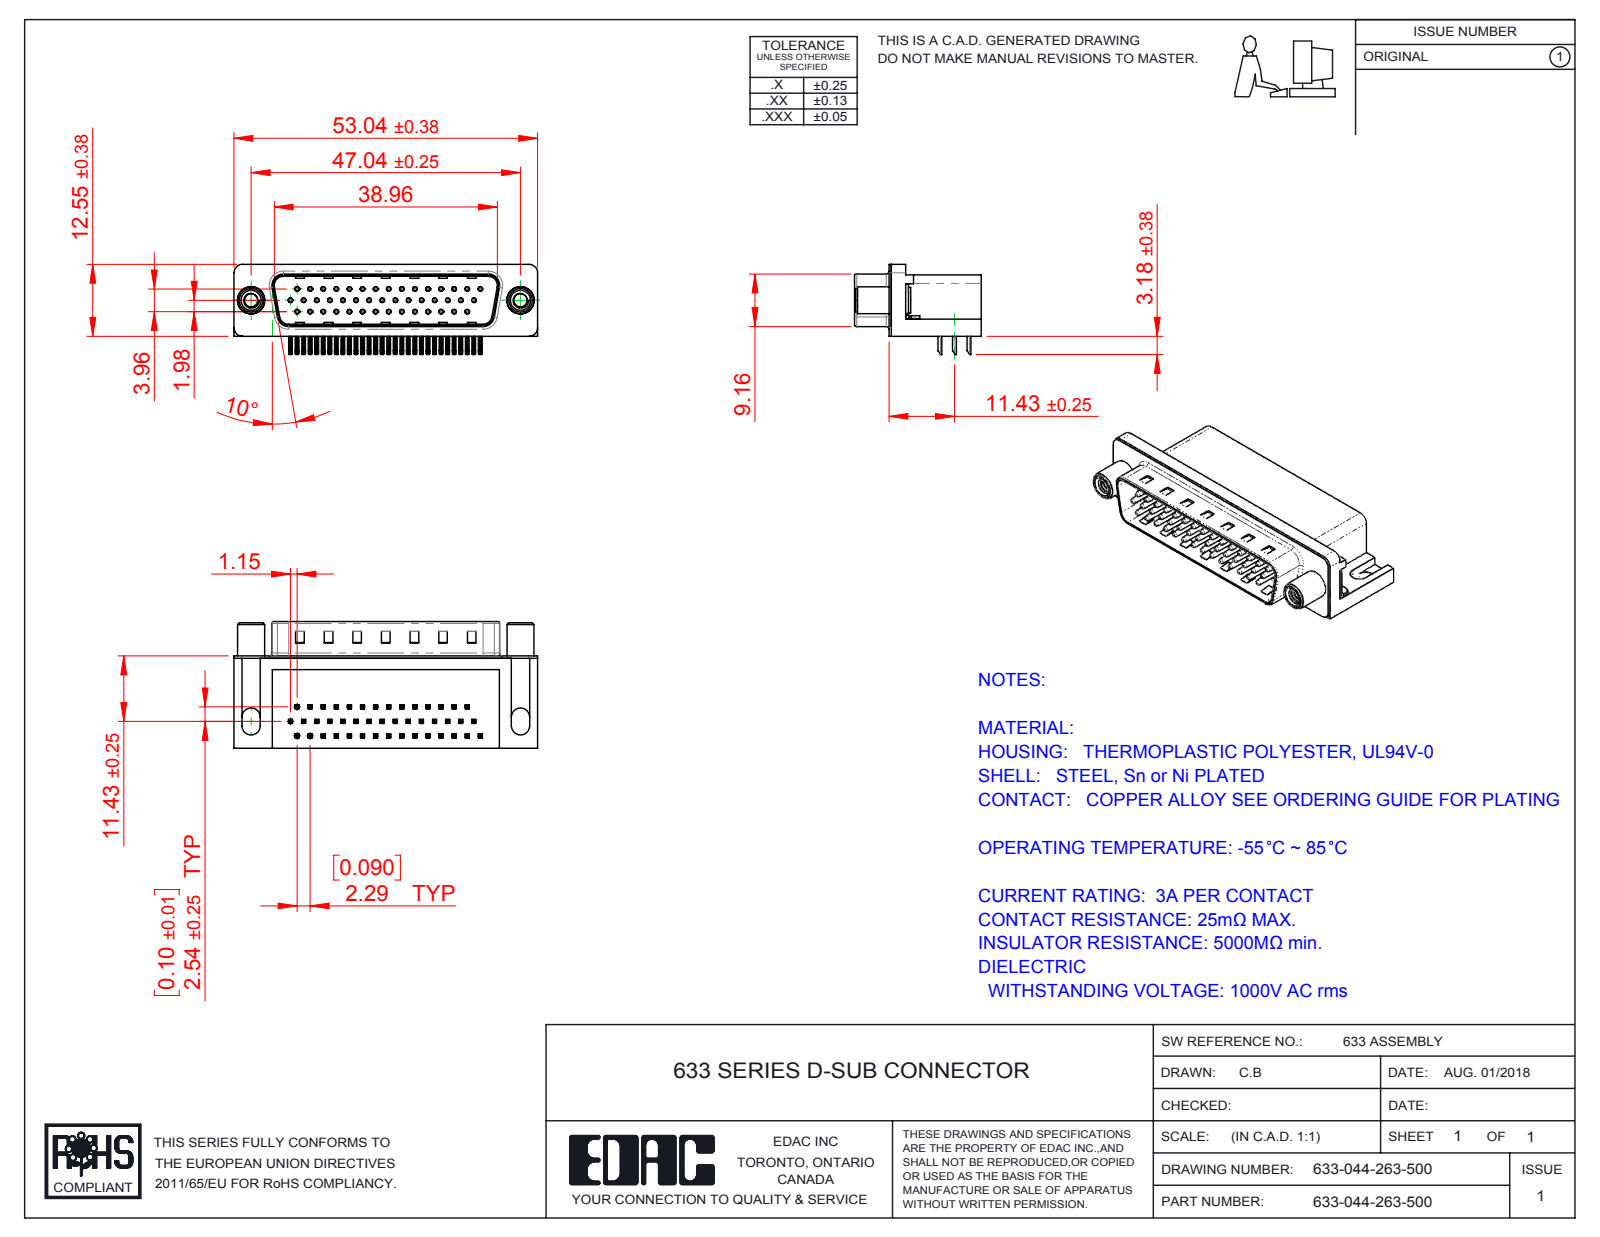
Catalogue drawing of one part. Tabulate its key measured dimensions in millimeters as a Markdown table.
| quantity | value |
| --- | --- |
| part name | 633 Non Board Mount; 633 Round Threaded Standoff; 633 Contact Middle; 633 Shell_44 Contact (+4 more) |
| STEP written by | SolidWorks 2016 (CONFIG_CONTROL_DESIGN) |
| units | millimeters |
| bodies | 50 solids, 3680 faces (2309 planar, 1064 cylindrical, 307 other) |
| overall size | 53.04 × 22.1 × 15.73 |
| volume | 8 158 mm³ |
| surface area | 10 194 mm² |
| round holes (diameter × count) | 0.35 × 44, 0.8 × 44, 2.3 × 2, 3.1 × 2, 4 × 2, 4.8 × 2, 5 × 2 |
| round bosses / shafts (diameter × count) | 0.75 × 44, 4.9 × 2, 4.7 × 2, 4.5 × 2, 3.85 × 2 |
| partial cylindrical surfaces (radius × count) | 0.25 × 176, 0.12 × 88, 1 × 16, 0.5 × 9, 1.6 × 8, 1.5 × 7, 0.9 × 4, 2 × 4 |
| main face-to-face distances | 0.4, 10.35, 15.7, 8.76, 2.9, 2.5, 2.1, 2.54, 16.1, 10.7 |
| hole center spacings | 2.29, 4.57, 4.58, 2.28, 6.87, 9.16, 11.45, 2.27 |
